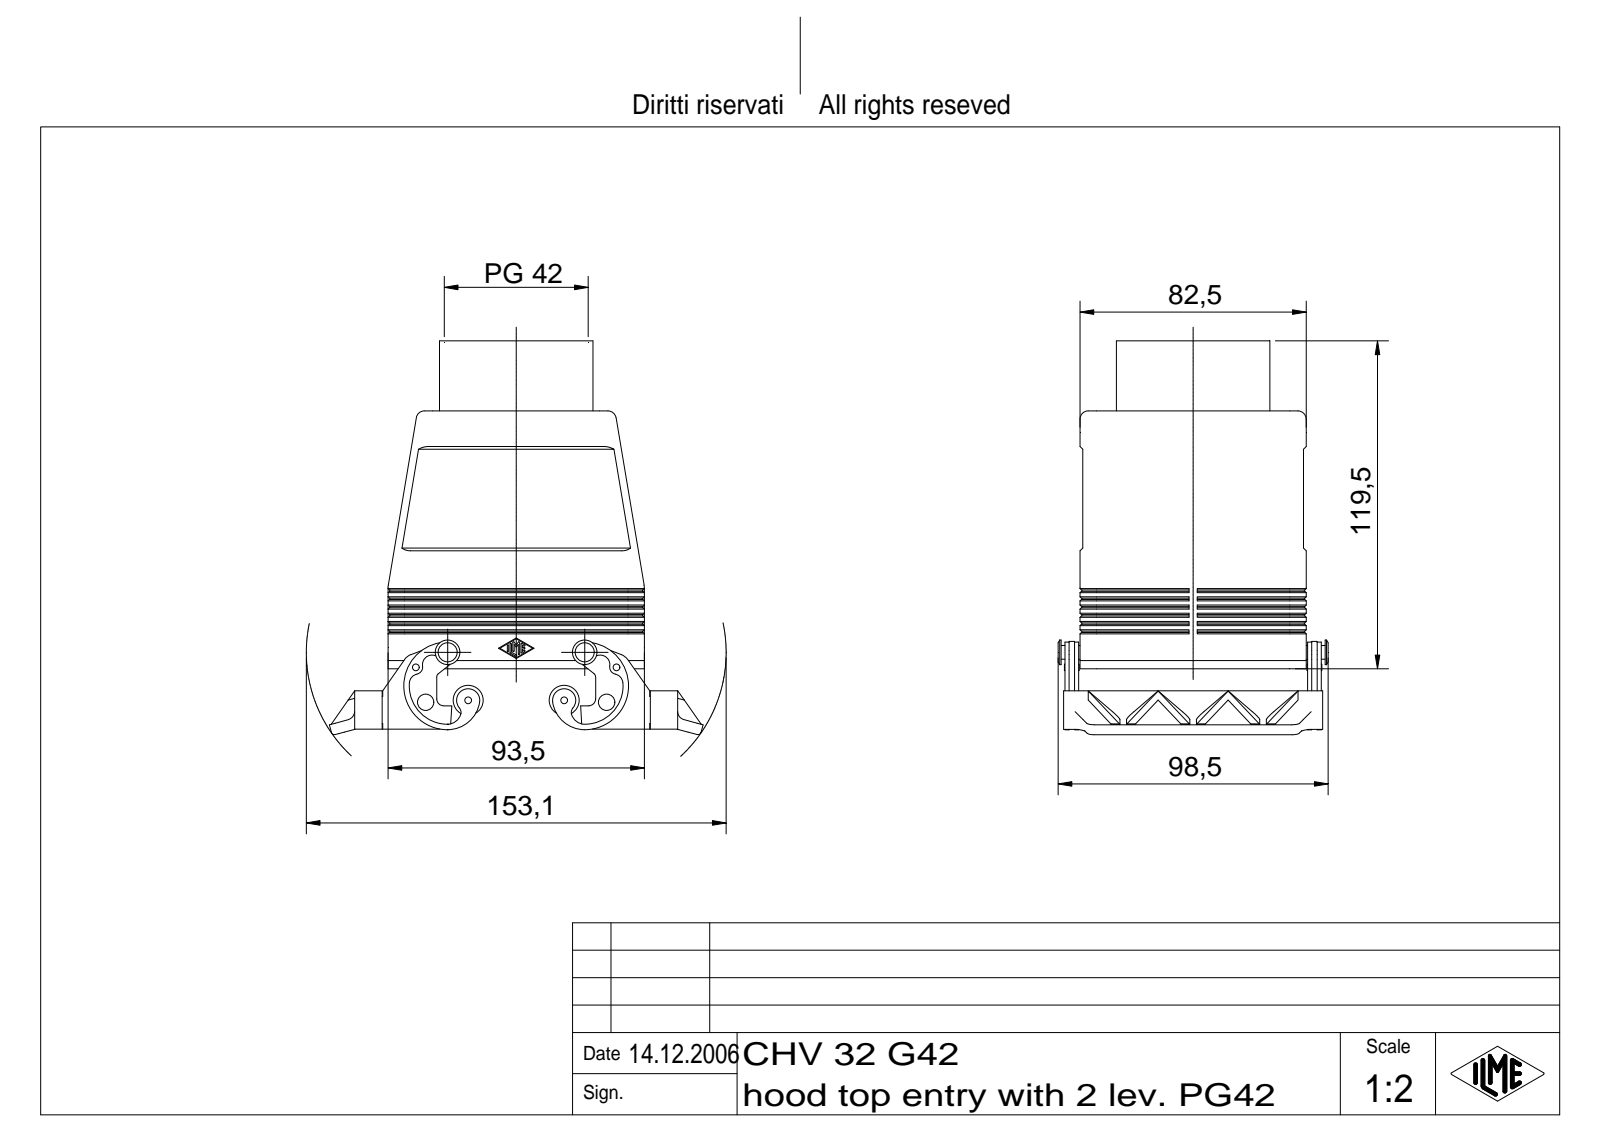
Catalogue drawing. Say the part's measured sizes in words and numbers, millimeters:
The part is named "CHV 32 G42". Its 3-D file was written by "Autodesk Inventor 7 (AUTOMOTIVE_DESIGN)". It is 1 solid with 1077 faces: 324 planar, 290 cylindrical and 463 other. Overall it measures 143.53 by 136.28 by 98.5 millimeters. Its volume is 181 031 cubic millimeters and its surface area 102 724 square millimeters. Round holes: 4 of diameter 2.46, 4 of diameter 3.5, 2 of diameter 2.5, 2 of diameter 6, 1 of diameter 50.48, 1 of diameter 52.48. Round bosses or shafts: 2 of diameter 11, 2 of diameter 9, 2 of diameter 5, 2 of diameter 2, 1 of diameter 65, 1 of diameter 56. Partial cylindrical surfaces (rounded edges, fillets, slot ends): 14 of radius 0.25, 14 of radius 3, 12 of radius 2, 10 of radius 6, 6 of radius 1, 6 of radius 2.5, 4 of radius 3.5, 4 of radius 5. The main face-to-face distances are 4, 82.5, 78.5, 74.5, 3, 71.5, 11, 1, 77.5, 81.5. The hole center spacings are 13.21, 27, 38.96, 49.62, 70.75, 77.5, 82.07, 66.
